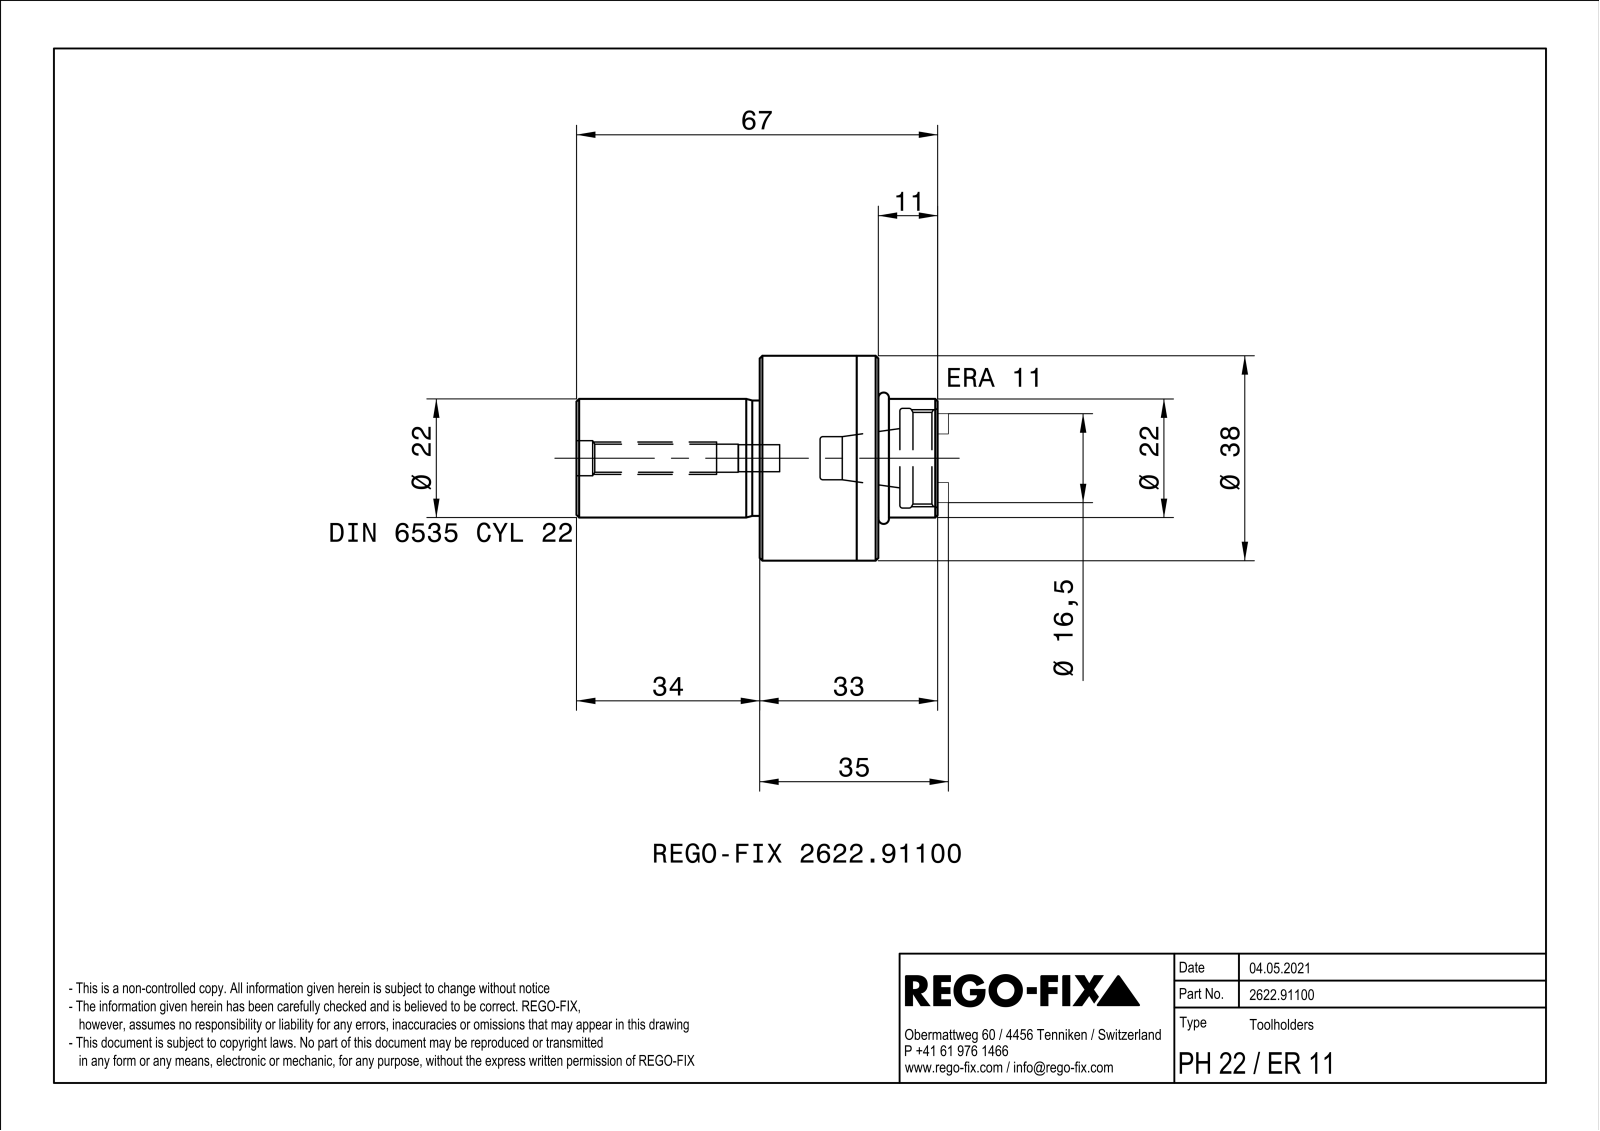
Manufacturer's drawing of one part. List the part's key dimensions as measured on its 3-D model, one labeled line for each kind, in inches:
Part name (STEP PRODUCT): NOCUT
STEP written by: SIEMENS PLM Software Solid Edge ST10 (AUTOMOTIVE_DESIGN)
Units: inches
Bodies: 1 solid, 99 faces (22 planar, 31 cylindrical, 46 other)
Overall size (bounding box): 2.638 × 1.496 × 1.496
Volume: 1.979 in³ · Surface area: 23.76 in²
Round holes (diameter × count): ⌀0.118 ×4, ⌀0.102 ×2, ⌀0.059 ×1, ⌀0.083 ×1, ⌀0.197 ×1, ⌀0.205 ×1, ⌀0.256 ×1, ⌀0.315 ×1, ⌀0.669 ×1, ⌀0.728 ×1, ⌀0.874 ×1, ⌀1.102 ×1
Round bosses / shafts (diameter × count): ⌀1.496 ×1, ⌀1.181 ×1, ⌀1.122 ×1, ⌀1.114 ×1, ⌀1.063 ×1, ⌀0.866 ×1, ⌀0.843 ×1, ⌀0.591 ×1
Main face-to-face distances: 0.157, 0.315, 0.866, 0.551, 0.394, 0.472, 0.236, 0.327, 0.146, 0.169
Hole centre spacings: 0.472, 0.668, 0.803, 0.177, 0.65, 0.945, 1.122, 1.299
